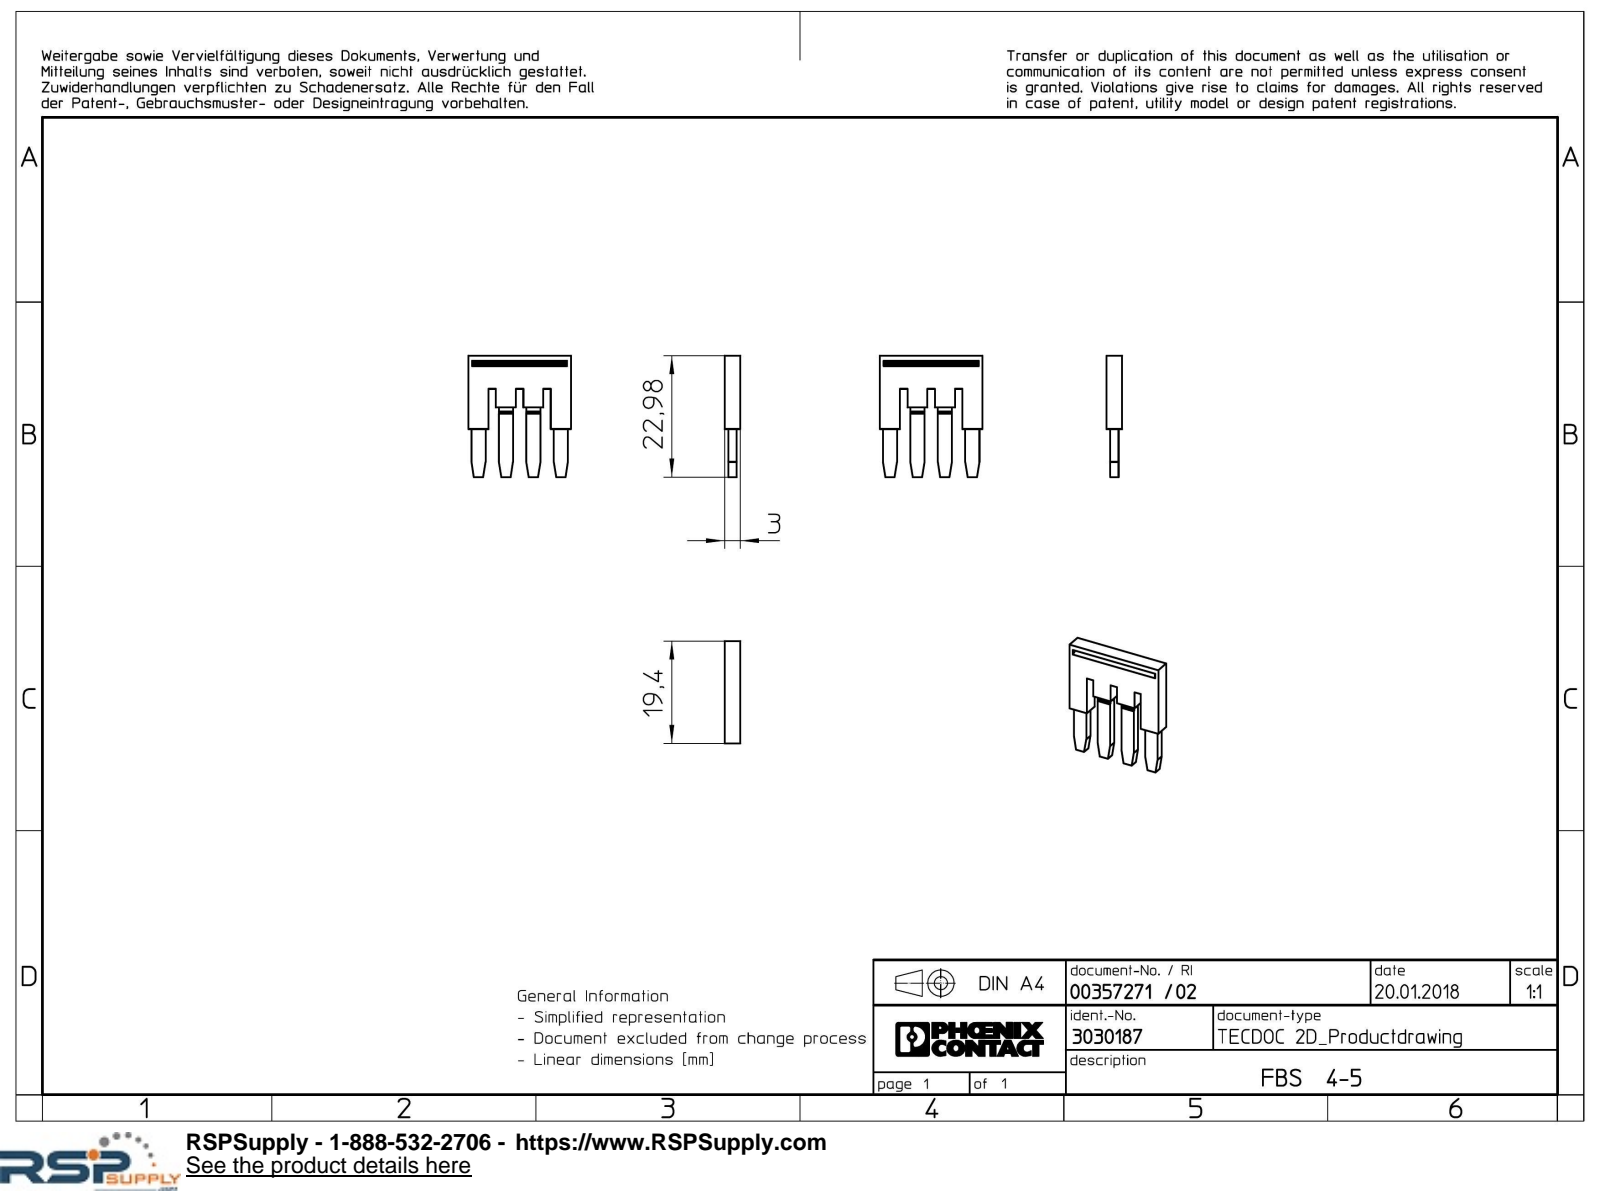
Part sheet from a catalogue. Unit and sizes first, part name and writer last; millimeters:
Units: millimetres
Overall size (bounding box): 22.98 × 19.4 × 3
Main face-to-face distances: 0.7, 2.3, 3, 5.2, 1.6, 0.56, 3.24, 10.4, 8.44, 4.64
Volume: 777 mm³ · Surface area: 1 123 mm²
Bodies: 1 solid, 68 faces (68 planar, 0 cylindrical, 0 other)
Part name (STEP PRODUCT): FBS_4_5-select
STEP written by: Creo Elements/Direct Modeling 20.1A 29-Sep-2018 (C) Parametric Technology GmbH (AUTOMOTIVE_DESIGN)
